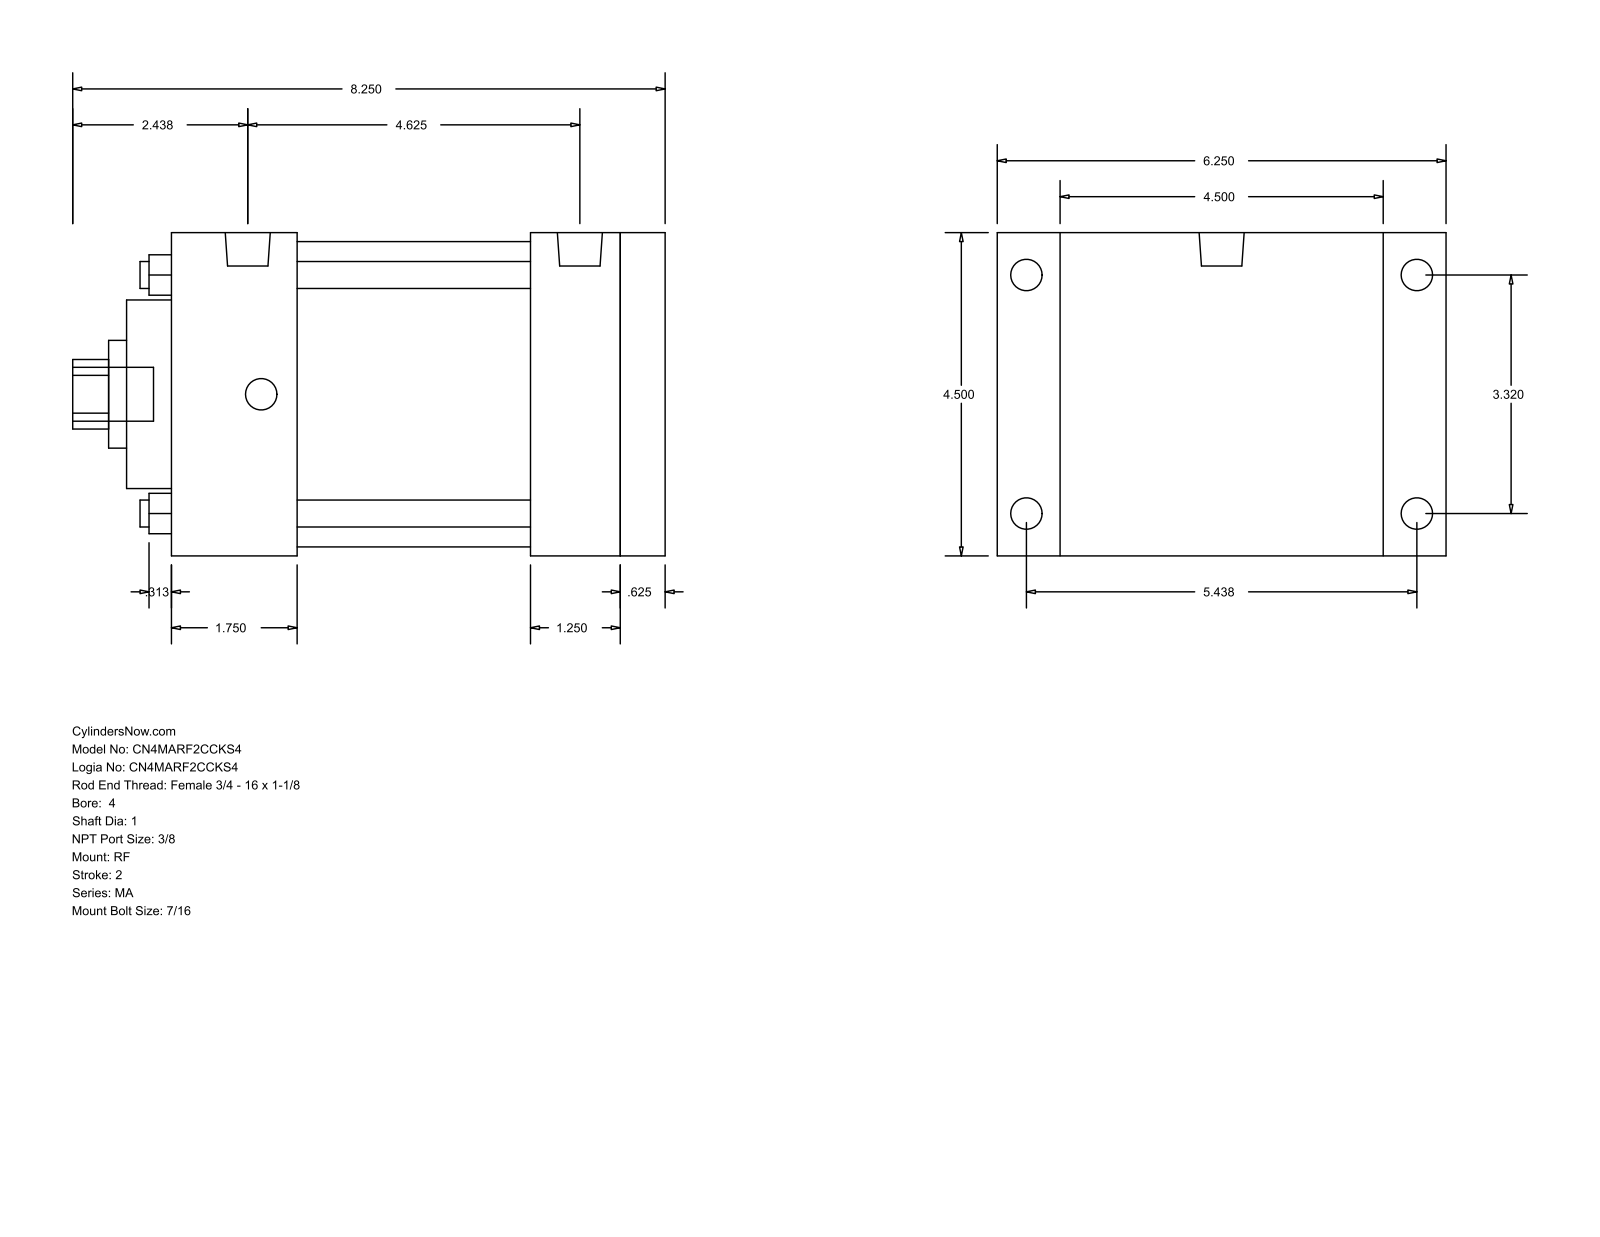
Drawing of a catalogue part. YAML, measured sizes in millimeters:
part_name: "MA_RF__0400_1"
step_written_by: "GSSL Pune (CONFIG_CONTROL_DESIGN)"
units: millimeters
bodies: {solids: 0, faces: 94, planar: 65, cylindrical: 29, other: 0}
overall_size: [209.55, 158.75, 114.3]
round_holes:
  - {diameter: 9.53, count: 4}
  - {diameter: 25.4, count: 1}
  - {diameter: 38.1, count: 1}
  - {diameter: 66.67, count: 1}
  - {diameter: 107.95, count: 1}
round_bosses_or_shafts:
  - {diameter: 11.11, count: 8}
  - {diameter: 15.93, count: 2}
  - {diameter: 19.05, count: 1}
partial_cylinders:
  - {radius: 12.29, count: 1}
face_to_face_distances: [114.3, 174.63, 15.87, 158.76, 22.23, 136.53, 127.01, 31.75, 47.62, 44.46]
hole_center_spacings: [59.62, 84.32, 119.25]
